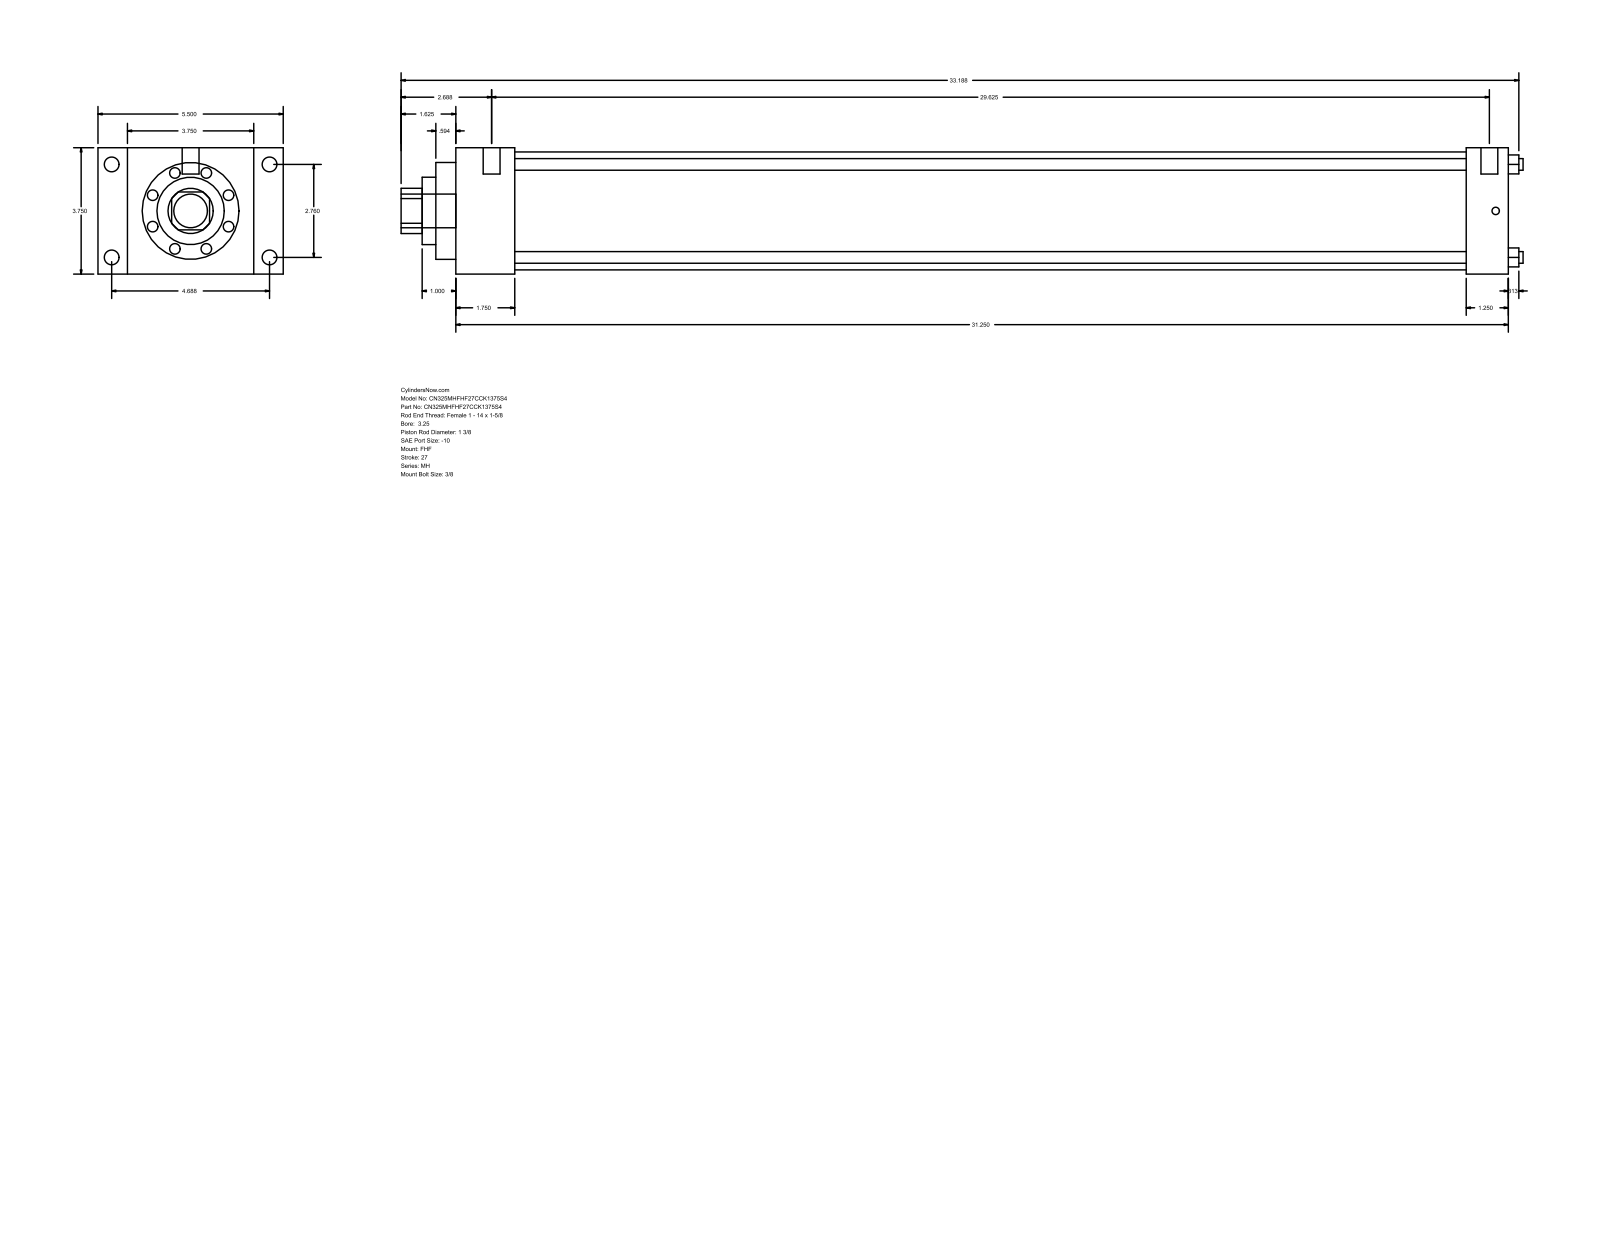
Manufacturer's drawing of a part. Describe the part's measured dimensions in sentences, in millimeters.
The part is named "MH_FHF__0325_1.375". Its 3-D file was written by "GSSL Pune (CONFIG_CONTROL_DESIGN)". It is 0 solids with 90 faces: 61 planar, 29 cylindrical and 0 other. Overall it measures 846.14 by 139.7 by 95.25 millimeters. Round holes: 4 of diameter 8.76, 1 of diameter 34.92, 1 of diameter 50.8, 1 of diameter 73.03, 1 of diameter 88.9. Round bosses or shafts: 4 of diameter 11.13, 4 of diameter 5.56, 2 of diameter 12.7, 1 of diameter 25.4. Partial cylindrical surfaces (rounded edges, fillets, slot ends): 1 of radius 17.06. The main face-to-face distances are 95.24, 793.75, 44.45, 749.3, 22.23, 117.47, 139.7, 762, 717.55, 31.75. The hole center spacings are 49.57, 70.1, 99.14.
